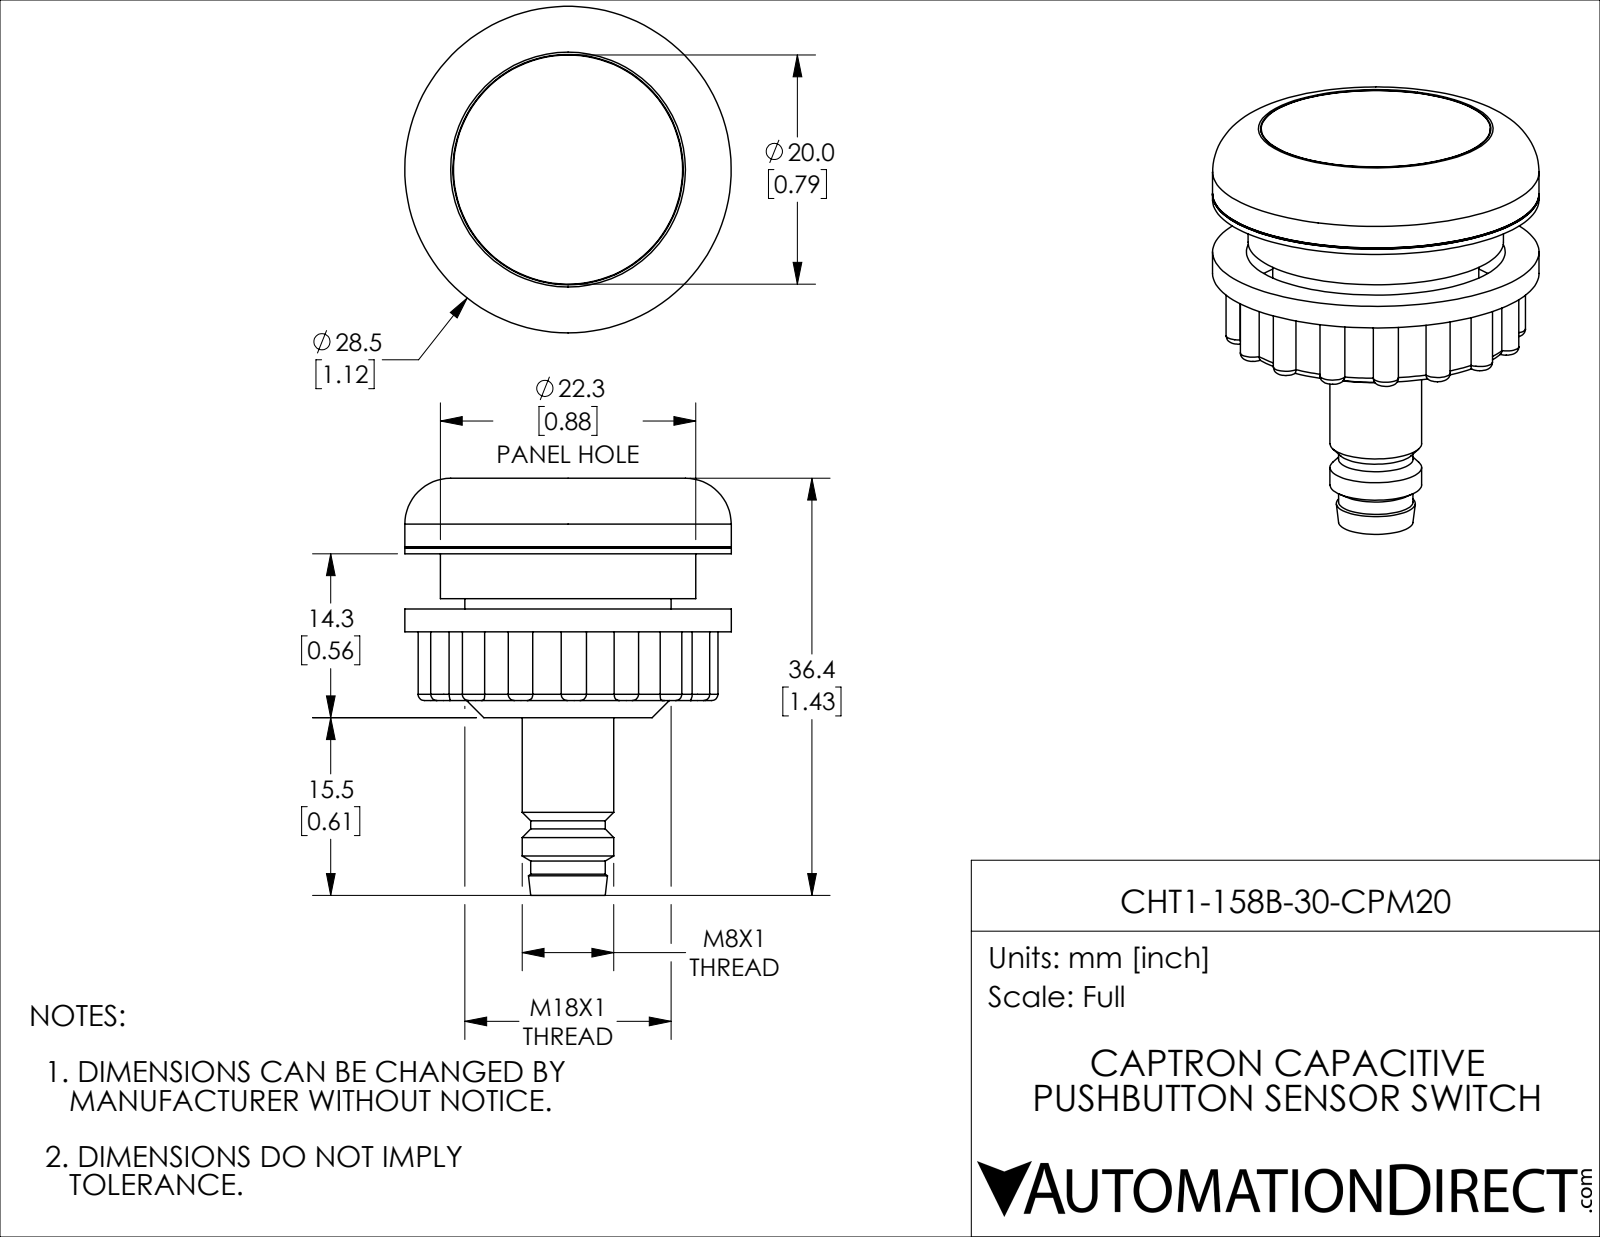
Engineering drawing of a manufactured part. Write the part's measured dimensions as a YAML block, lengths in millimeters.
part_name: "CHT1-158B-30-CPM20"
step_written_by: "SolidWorks 2019 (CONFIG_CONTROL_DESIGN)"
units: millimeters
bodies: {solids: 15, faces: 232, planar: 45, cylindrical: 90, other: 97}
overall_size: [36.4, 28.5, 28.5]
volume: 7381
surface_area: 9165
round_holes:
  - {diameter: 14.7, count: 1}
  - {diameter: 17, count: 1}
  - {diameter: 20.1, count: 1}
  - {diameter: 22.6, count: 1}
round_bosses_or_shafts:
  - {diameter: 1, count: 5}
  - {diameter: 28.5, count: 1}
  - {diameter: 22.3, count: 1}
  - {diameter: 18, count: 1}
  - {diameter: 14.4, count: 1}
  - {diameter: 14, count: 1}
  - {diameter: 8, count: 1}
  - {diameter: 6.5, count: 1}
partial_cylinders:
  - {radius: 1.1, count: 16}
  - {radius: 1, count: 1}
  - {radius: 2.9, count: 1}
  - {radius: 12, count: 1}
face_to_face_distances: [3, 6, 14.6, 14.7, 5.3, 9.3, 20.7, 6.1, 1.5, 13.1]
